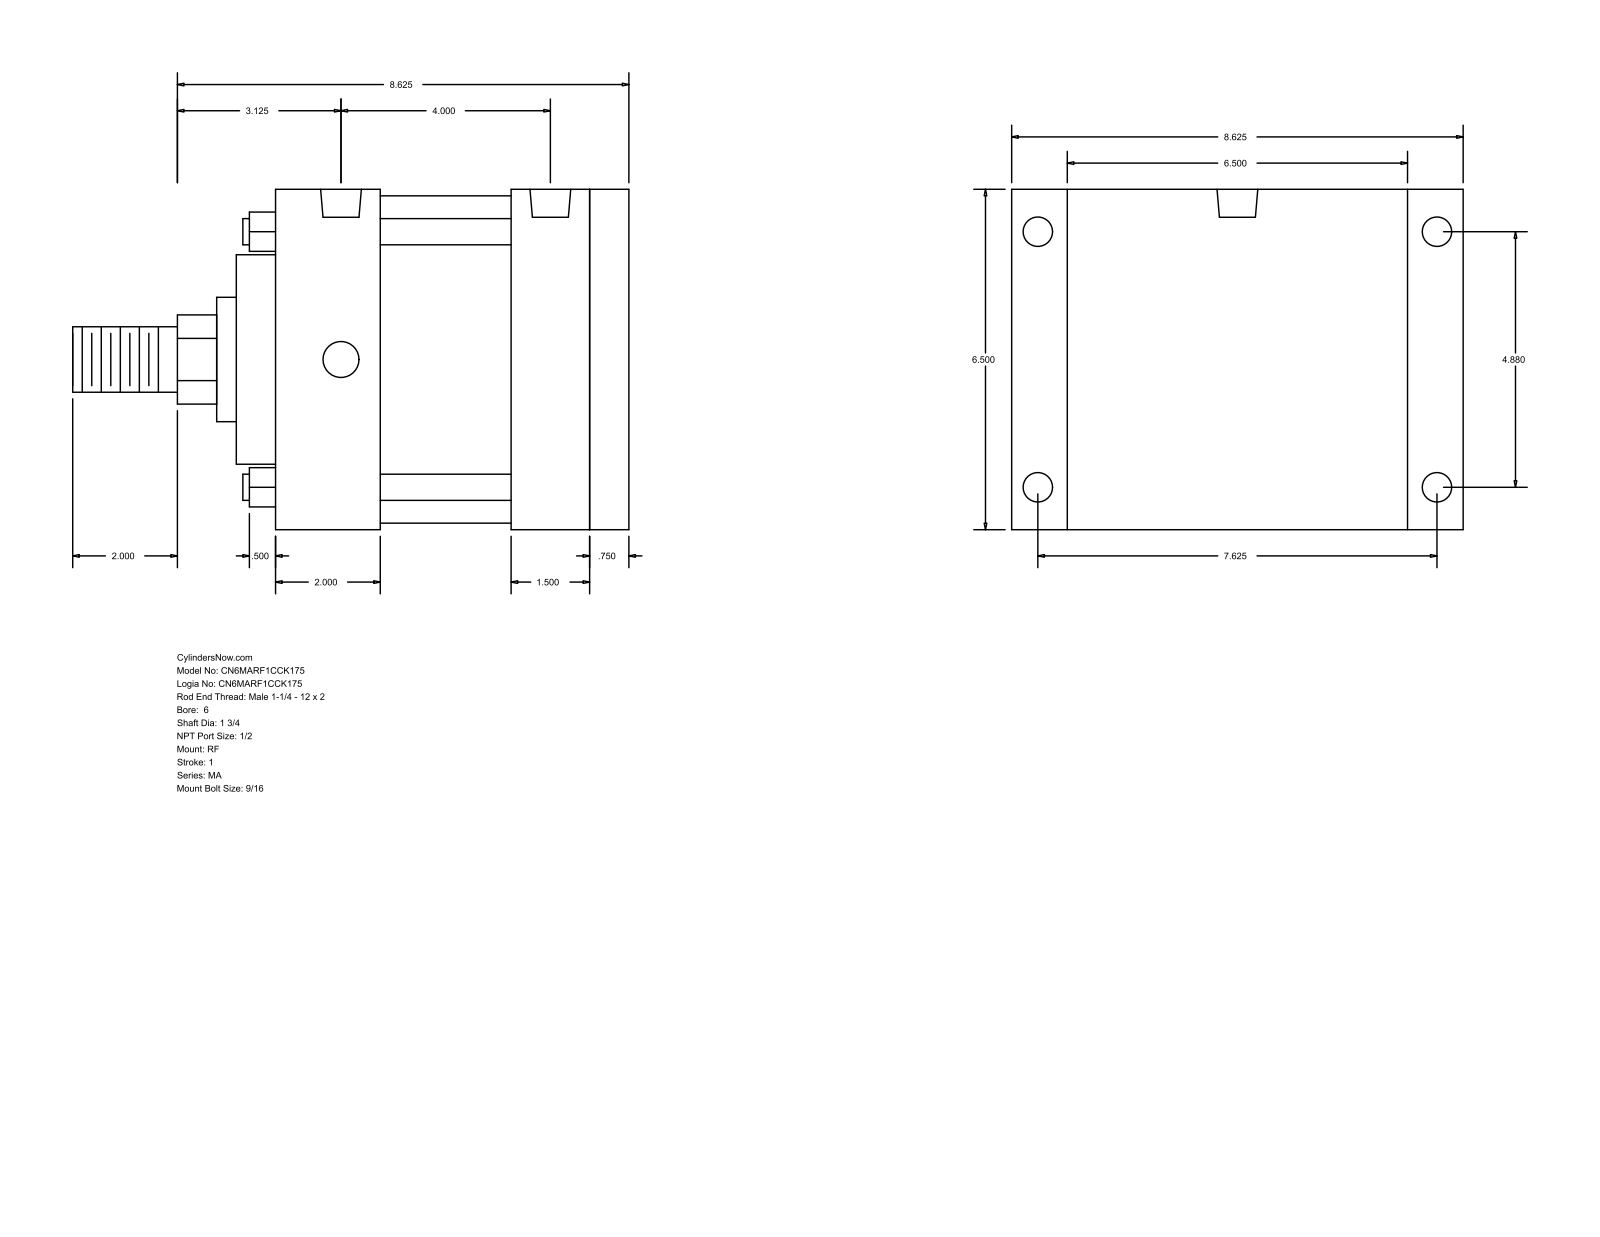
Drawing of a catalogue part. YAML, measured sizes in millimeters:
part_name: "MA_RF__0600_1.75"
step_written_by: "GSSL Pune (CONFIG_CONTROL_DESIGN)"
units: millimeters
bodies: {solids: 0, faces: 94, planar: 65, cylindrical: 29, other: 0}
overall_size: [269.88, 219.07, 165.1]
round_holes:
  - {diameter: 14.29, count: 4}
  - {diameter: 17.46, count: 4}
  - {diameter: 19.77, count: 2}
round_bosses_or_shafts:
  - {diameter: 12.7, count: 4}
  - {diameter: 158.75, count: 1}
  - {diameter: 101.6, count: 1}
  - {diameter: 60.33, count: 1}
  - {diameter: 44.45, count: 1}
  - {diameter: 31.75, count: 1}
partial_cylinders:
  - {radius: 21.63, count: 1}
face_to_face_distances: [165.1, 171.45, 19.04, 152.41, 38.1, 50.8, 19.05, 101.61, 120.65, 114.31]
hole_center_spacings: [101.59, 123.96, 193.68, 229.95]
